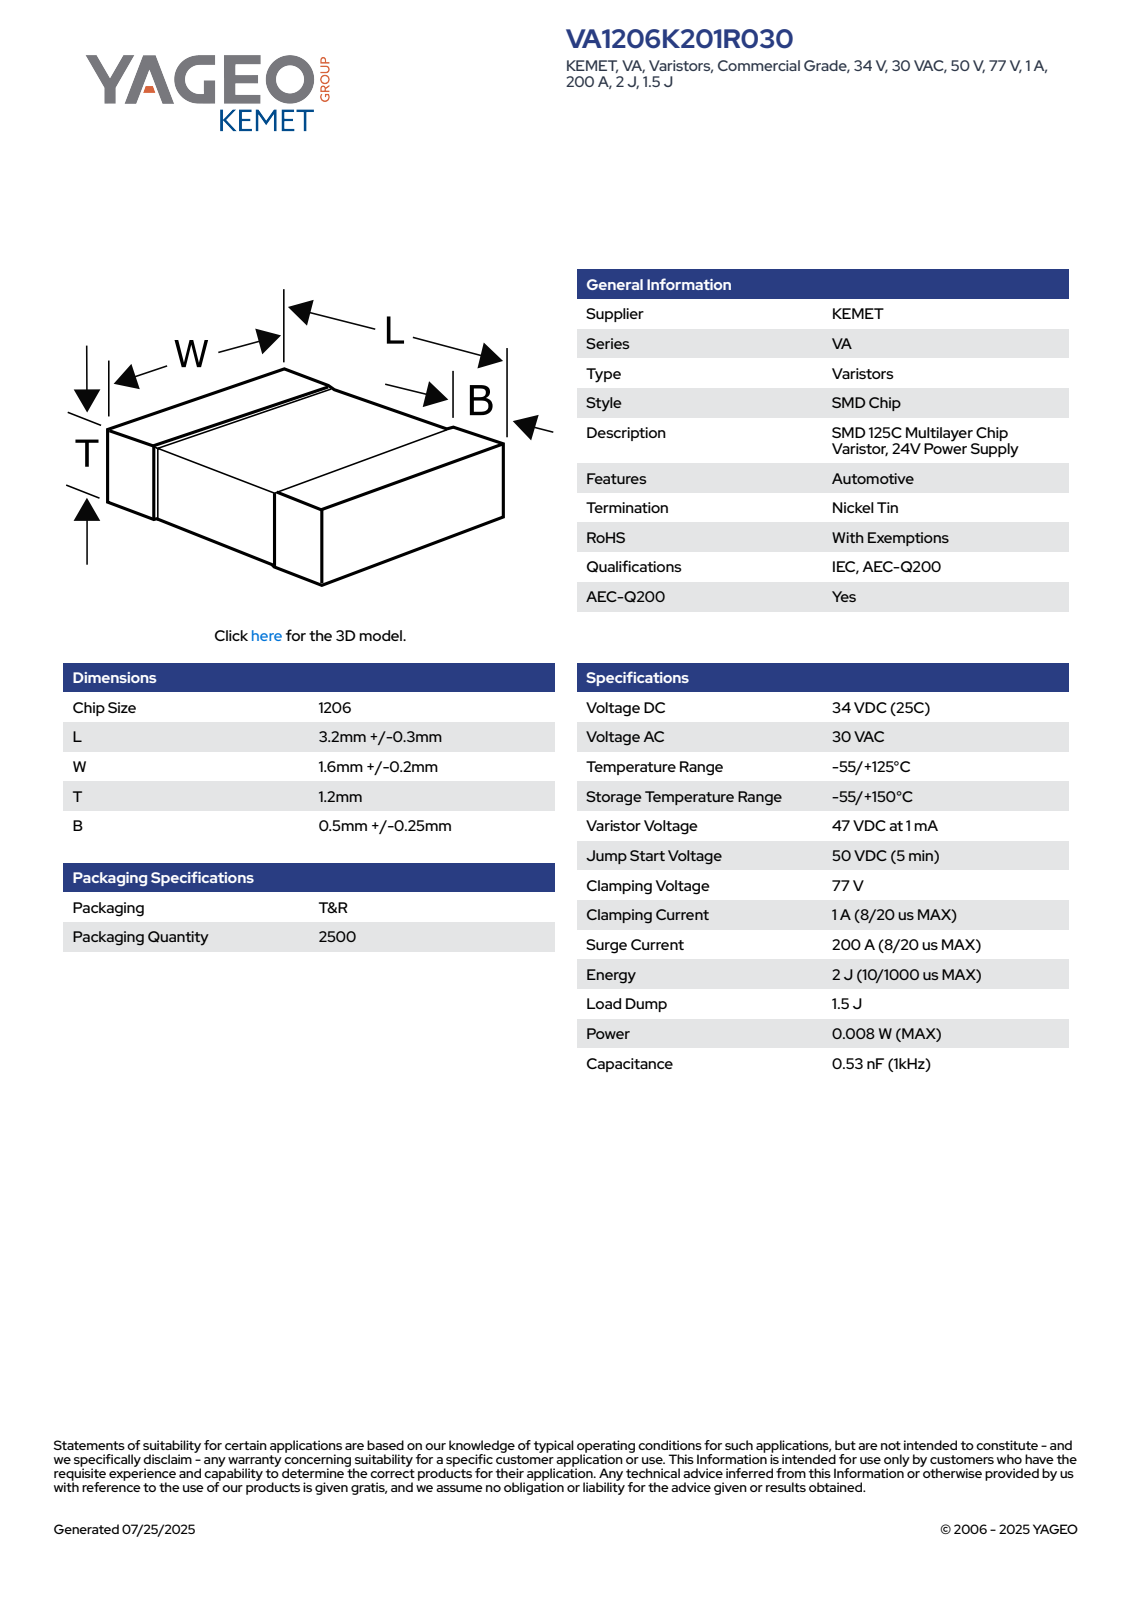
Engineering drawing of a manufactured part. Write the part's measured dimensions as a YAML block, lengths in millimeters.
part_name: "VS_SMD_1206_L3.50W1.8T1.2B0.75"
step_written_by: "SolidWorks 2014 (AUTOMOTIVE_DESIGN)"
units: millimeters
bodies: {solids: 4, faces: 125, planar: 71, cylindrical: 38, other: 16}
overall_size: [3.5, 1.8, 1.2]
volume: 7
surface_area: 25
face_to_face_distances: [1.16, 1.12, 1.76, 1.2, 1.72, 3.5, 1.8, 1.17, 1.13, 1.63]
